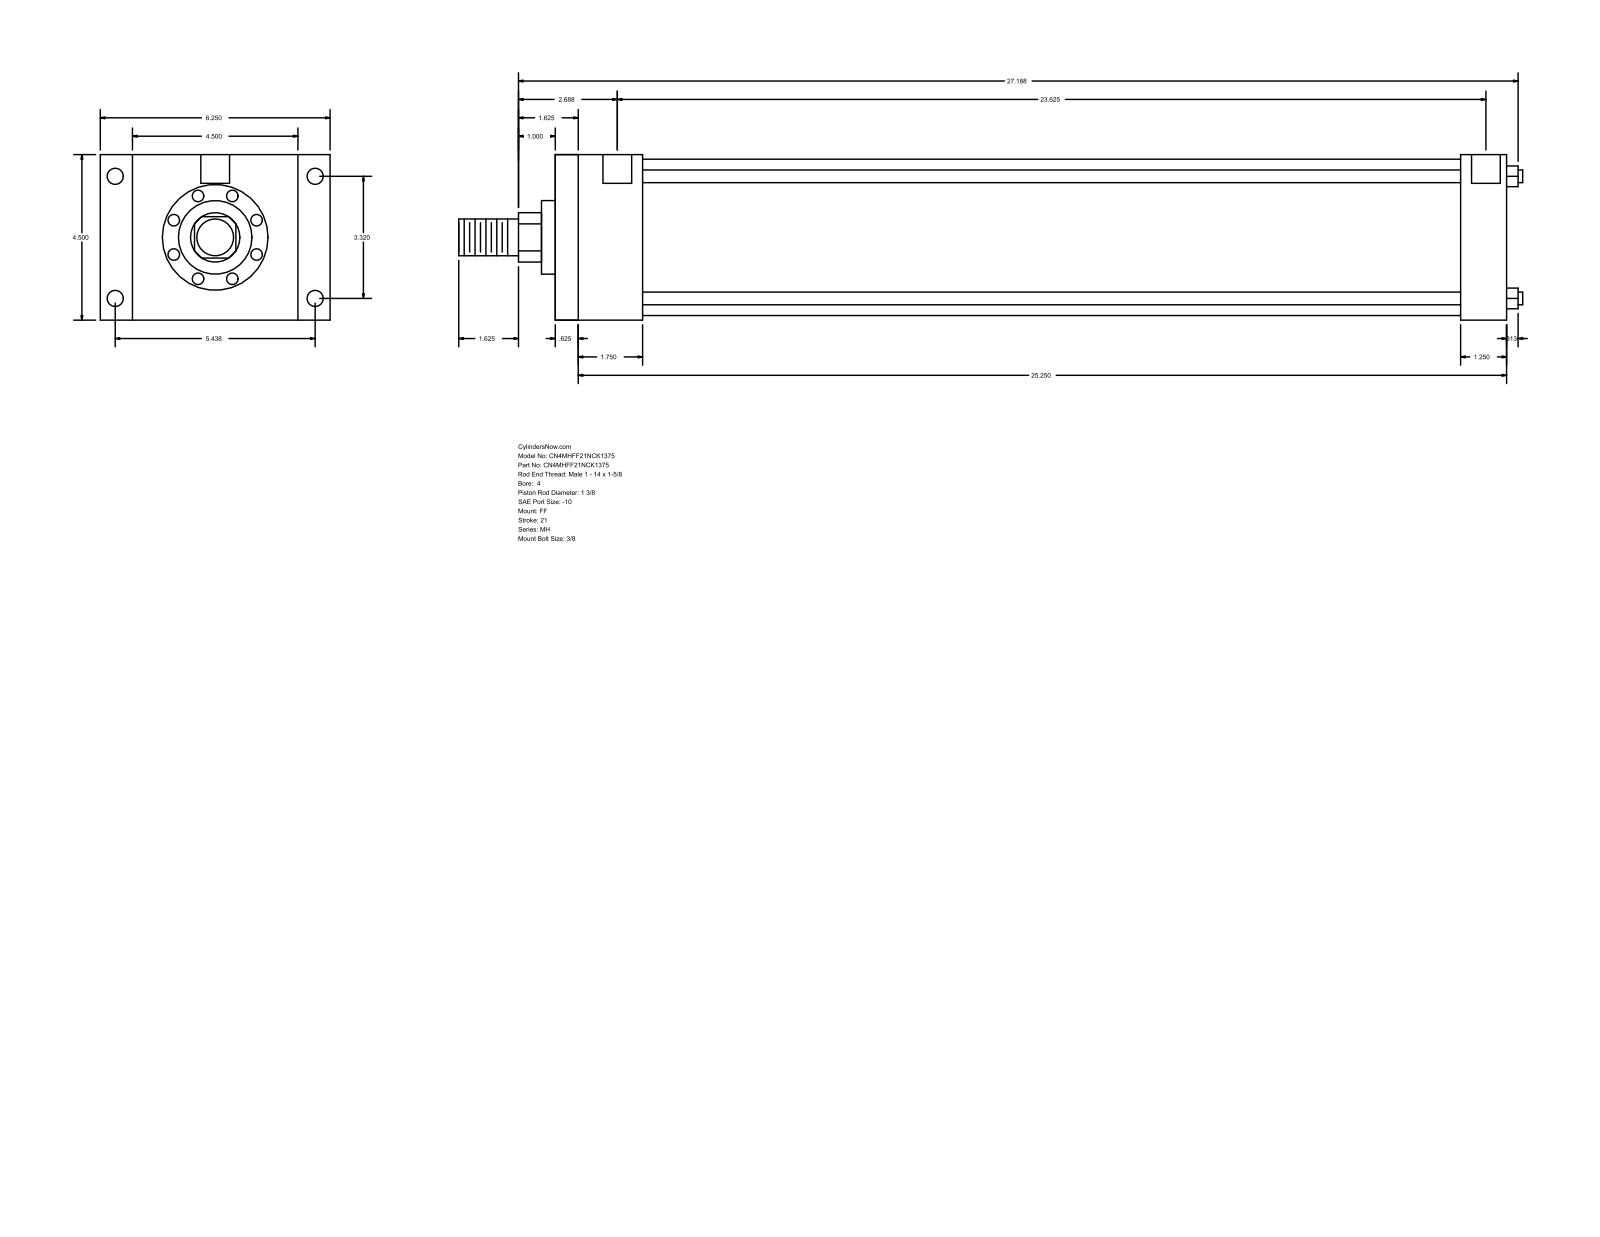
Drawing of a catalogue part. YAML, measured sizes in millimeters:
part_name: "MH_FF__0400_1.375"
step_written_by: "GSSL Pune (CONFIG_CONTROL_DESIGN)"
units: millimeters
bodies: {solids: 0, faces: 92, planar: 64, cylindrical: 28, other: 0}
overall_size: [735.01, 158.75, 114.3]
round_holes:
  - {diameter: 8.73, count: 4}
  - {diameter: 11.13, count: 4}
  - {diameter: 19.84, count: 2}
round_bosses_or_shafts:
  - {diameter: 8.76, count: 4}
  - {diameter: 107.95, count: 1}
  - {diameter: 50.8, count: 1}
  - {diameter: 34.92, count: 1}
  - {diameter: 25.4, count: 1}
partial_cylinders:
  - {radius: 17.06, count: 1}
face_to_face_distances: [114.3, 657.22, 15.87, 641.35, 60.32, 44.45, 596.9, 625.48, 609.61, 565.16]
hole_center_spacings: [84.32, 138.12, 161.82, 603.25, 1.58, 1.59, 600.08, 601.66]
